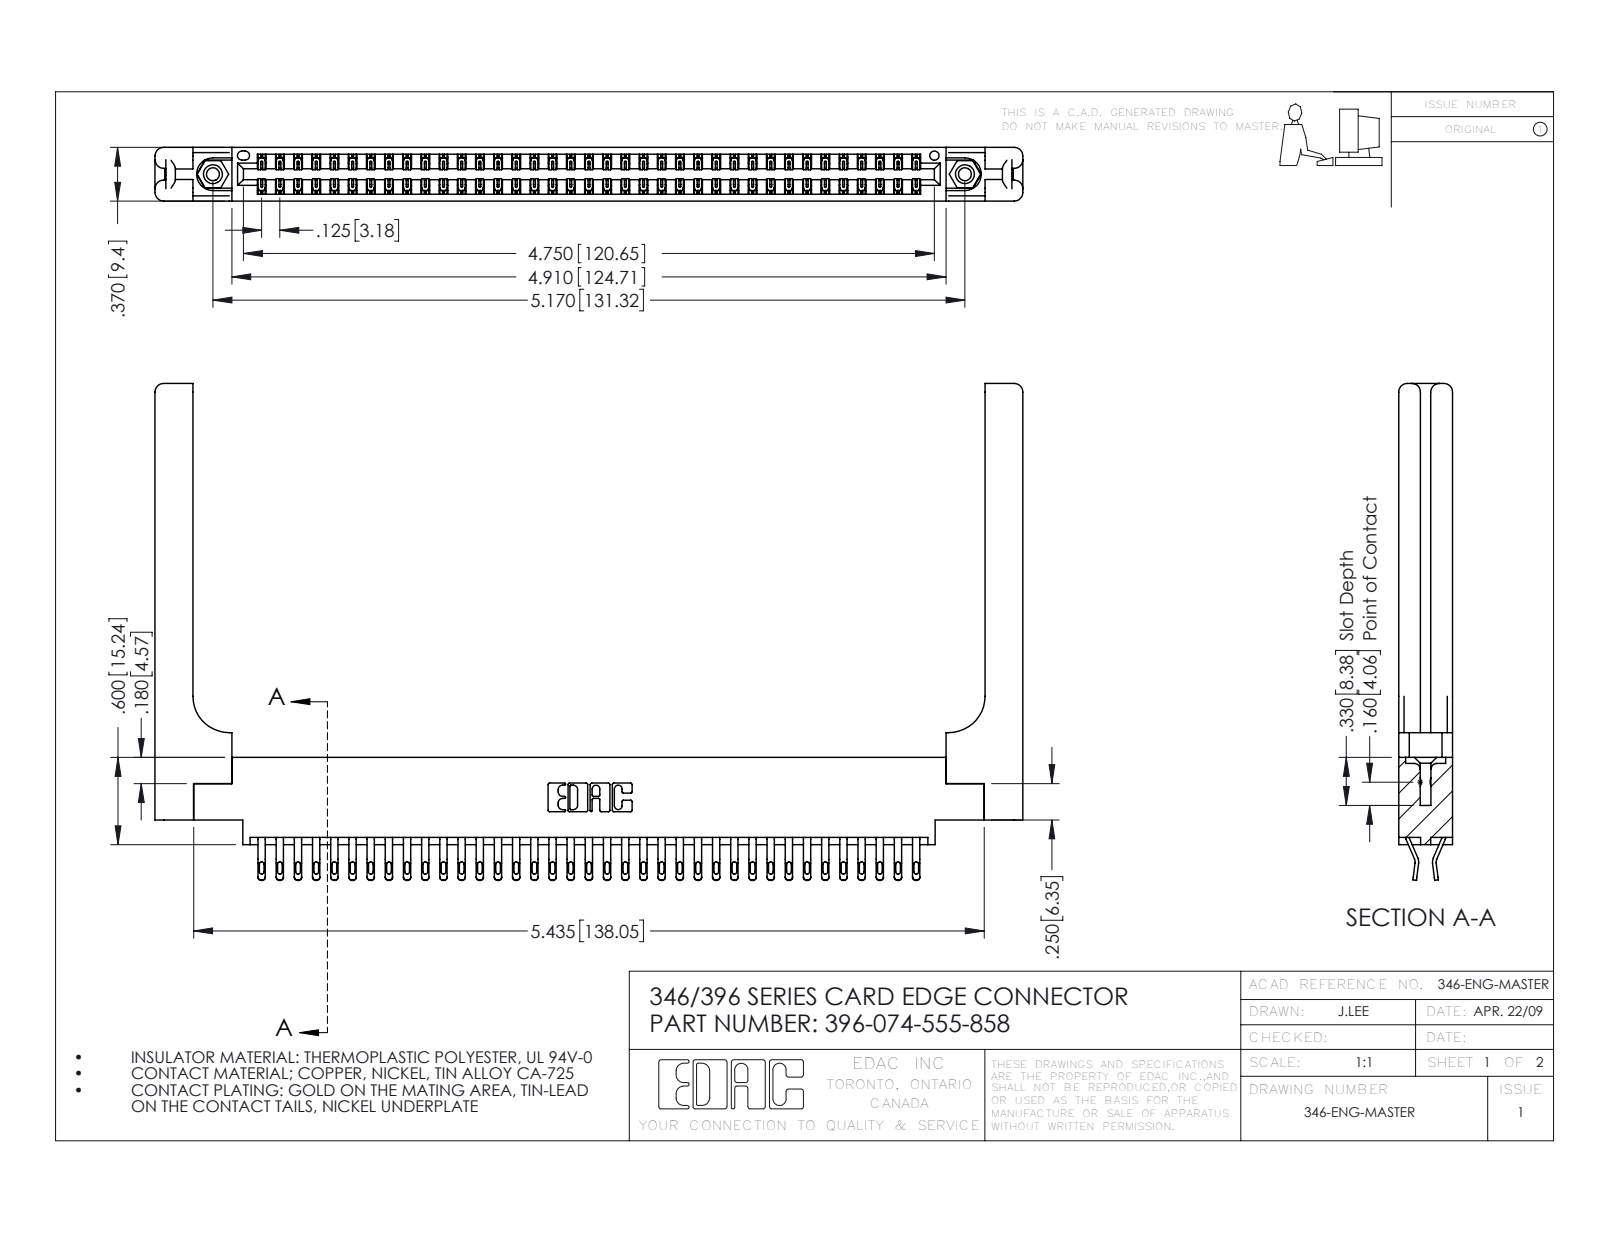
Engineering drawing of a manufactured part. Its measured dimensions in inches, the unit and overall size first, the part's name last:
Units: inches
Overall size (bounding box): 5.966 × 3.415 × 0.37
Round holes (diameter × count): ⌀0.089 ×2, ⌀0.125 ×2, ⌀0.156 ×2, ⌀0.064 ×1
Round bosses / shafts (diameter × count): ⌀0.155 ×2
Partial cylindrical surfaces — rounded edges, fillets, slot ends (radius × count): R0.016 ×148, R0.02 ×148, R0.006 ×111, R0.01 ×22, R0.06 ×16, R0.007 ×6, R0.031 ×6, R0.026 ×3
Main face-to-face distances: 0.37, 0.048, 0.322, 0.072, 0.148, 0.15, 0.25, 0.025, 0.298, 0.275
Hole centre spacings: 0.246, 4.961, 5.17
Volume: 1.36 in³ · Surface area: 40.58 in²
Bodies: 79 solids, 4674 faces (2670 planar, 1944 cylindrical, 60 other)
Part name (STEP PRODUCT): 346-220-058_345-220-058; 346 Part_0.170 Offset - 0.156 Dia-TH; 345-292-001_555 Tail; 345-250-001_345-250-001-102 (+1 more)
STEP written by: SolidWorks 2016 (CONFIG_CONTROL_DESIGN)
